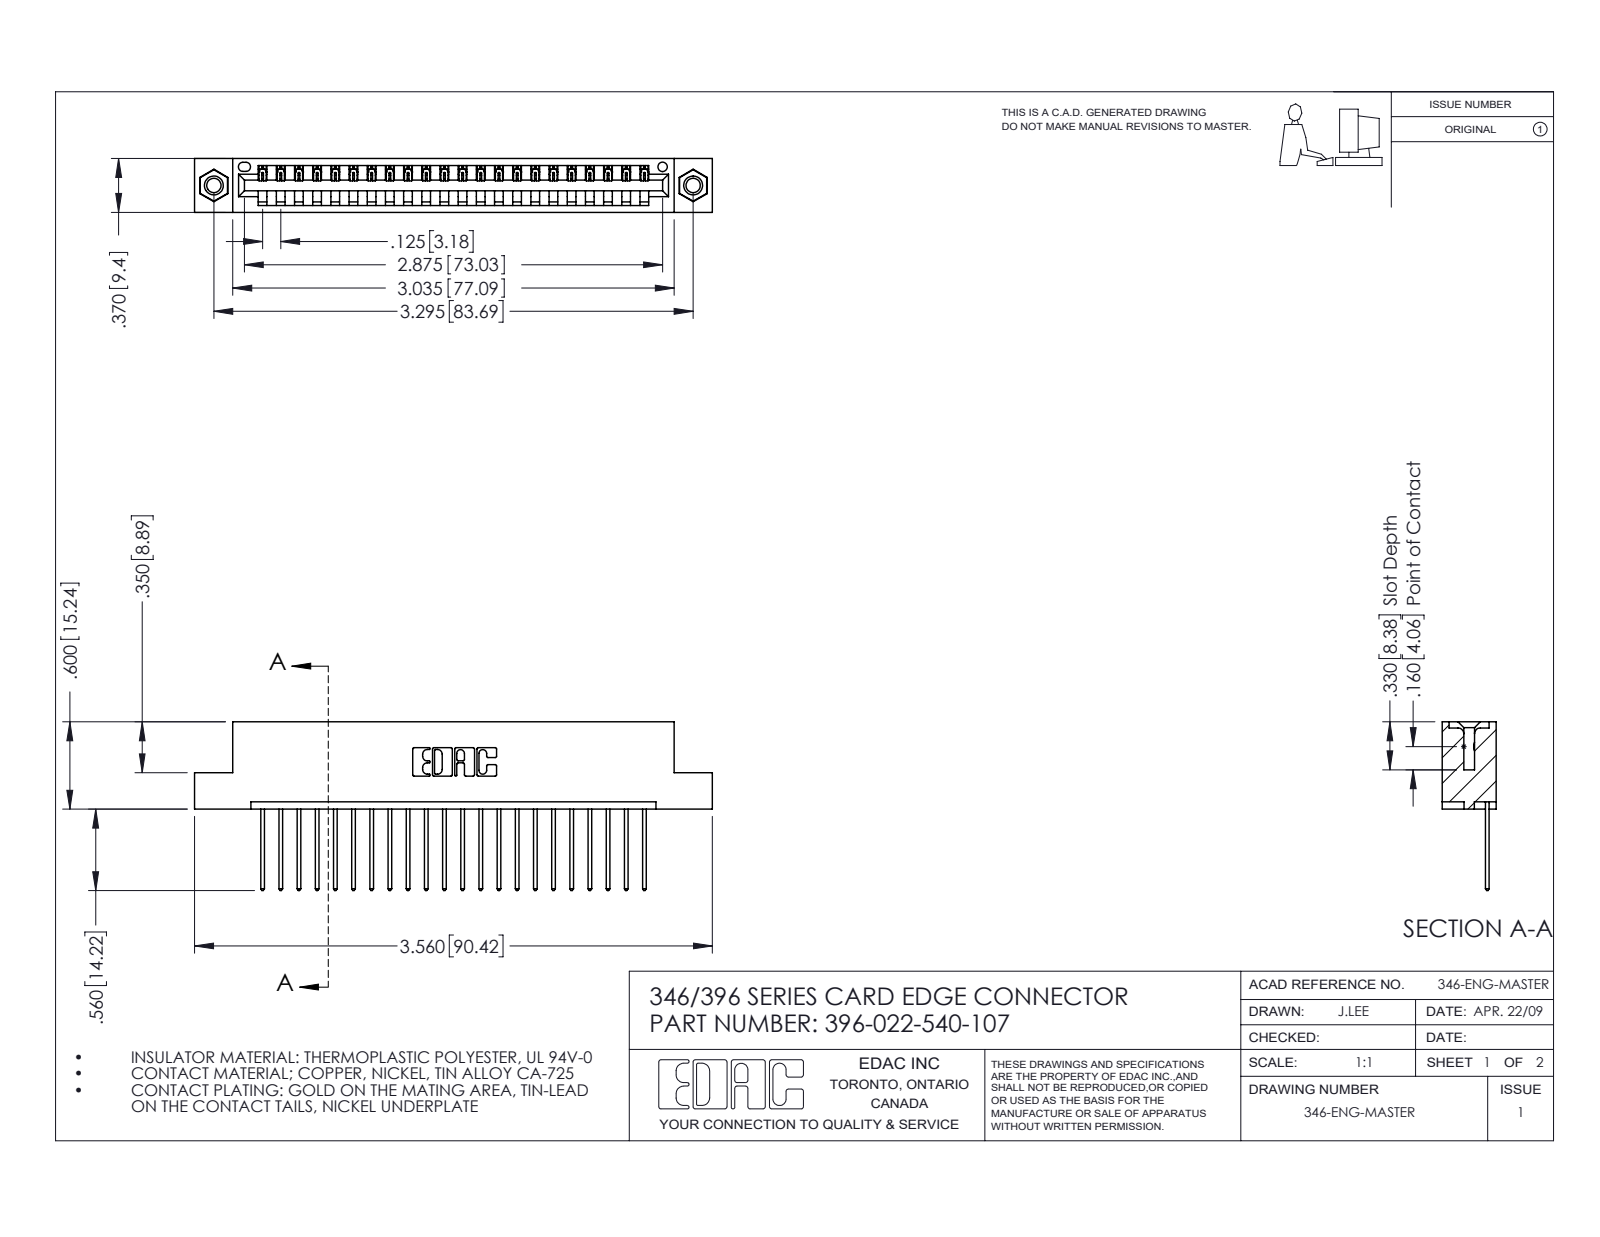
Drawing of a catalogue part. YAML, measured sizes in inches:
part_name: "345-292-001_345-293-140; 396-022-540-107; 346 Part_Flush Mounting Lugs - 0.156 Dia-TI; 345-250-001_345-250-005-103"
step_written_by: "SolidWorks 2016 (CONFIG_CONTROL_DESIGN)"
units: inches
bodies: {solids: 25, faces: 1458, planar: 988, cylindrical: 454, other: 16}
overall_size: [3.56, 1.16, 0.37]
volume: 0.521
surface_area: 16.59
round_holes:
  - {diameter: 0.098, count: 2}
  - {diameter: 0.125, count: 2}
  - {diameter: 0.156, count: 2}
  - {diameter: 0.064, count: 1}
round_bosses_or_shafts:
  - {diameter: 0.155, count: 2}
partial_cylinders:
  - {radius: 0.006, count: 44}
  - {radius: 0.01, count: 44}
  - {radius: 0.01, count: 22}
  - {radius: 0.007, count: 6}
  - {radius: 0.031, count: 6}
  - {radius: 0.026, count: 3}
  - {radius: 0.031, count: 2}
  - {radius: 0.04, count: 2}
face_to_face_distances: [0.048, 0.322, 0.25, 0.37, 0.072, 0.298, 0.025, 0.148, 0.222, 0.1]
hole_center_spacings: [0.246, 3.087, 3.295]
